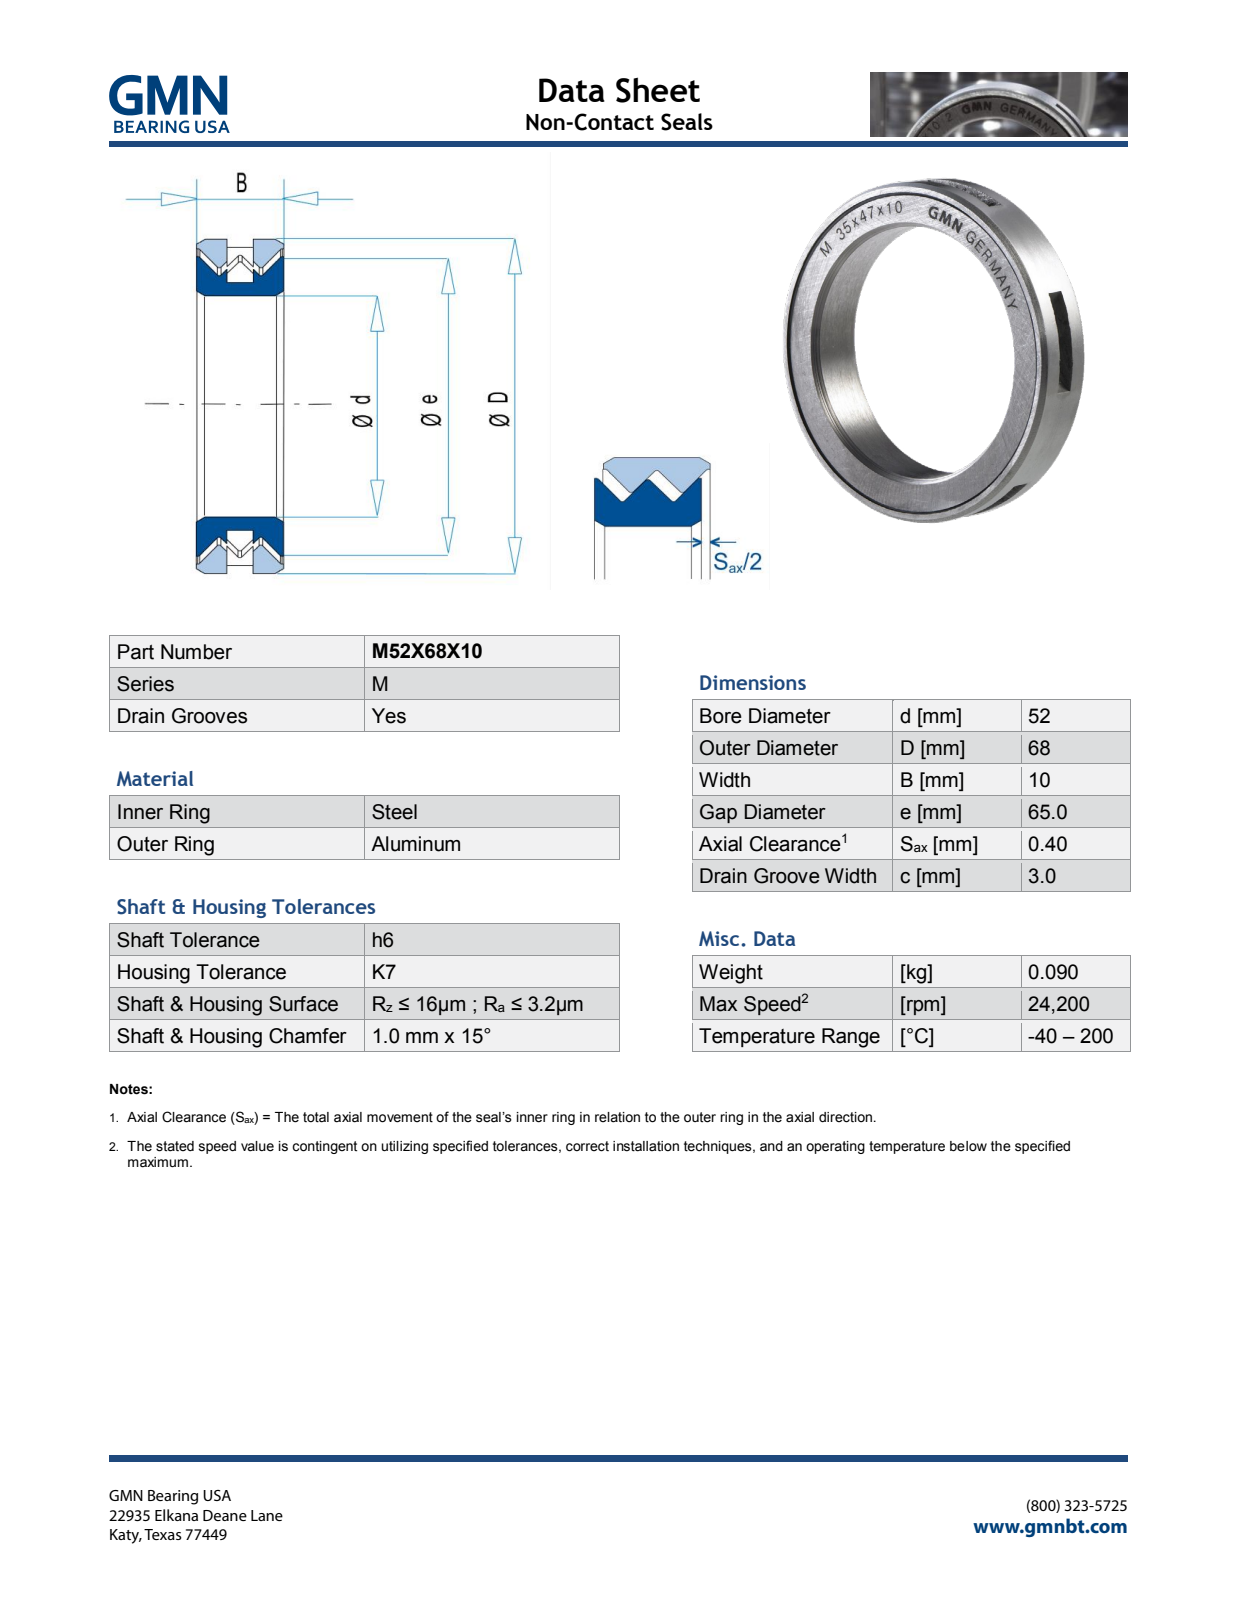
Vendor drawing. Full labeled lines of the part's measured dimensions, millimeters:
Part name (STEP PRODUCT): M52X68X10_PRT
STEP written by: PRO/ENGINEER BY PARAMETRIC TECHNOLOGY CORPORATION, 2013150 (AUTOMOTIVE_DESIGN)
Units: millimetres
Bodies: 2 solids, 670 faces (593 planar, 27 cylindrical, 50 other)
Overall size (bounding box): 68 × 68 × 10.07
Volume: 13 696 mm³ · Surface area: 11 791 mm²
Round holes (diameter × count): ⌀52 ×1, ⌀65.28 ×1
Round bosses / shafts (diameter × count): ⌀68 ×1, ⌀65 ×1
Partial cylindrical surfaces — rounded edges, fillets, slot ends (radius × count): R10 ×5
Main face-to-face distances: 10, 3.5, 6.5, 3, 3.57, 6.57, 10.07, 0.49, 3.92, 3.43
